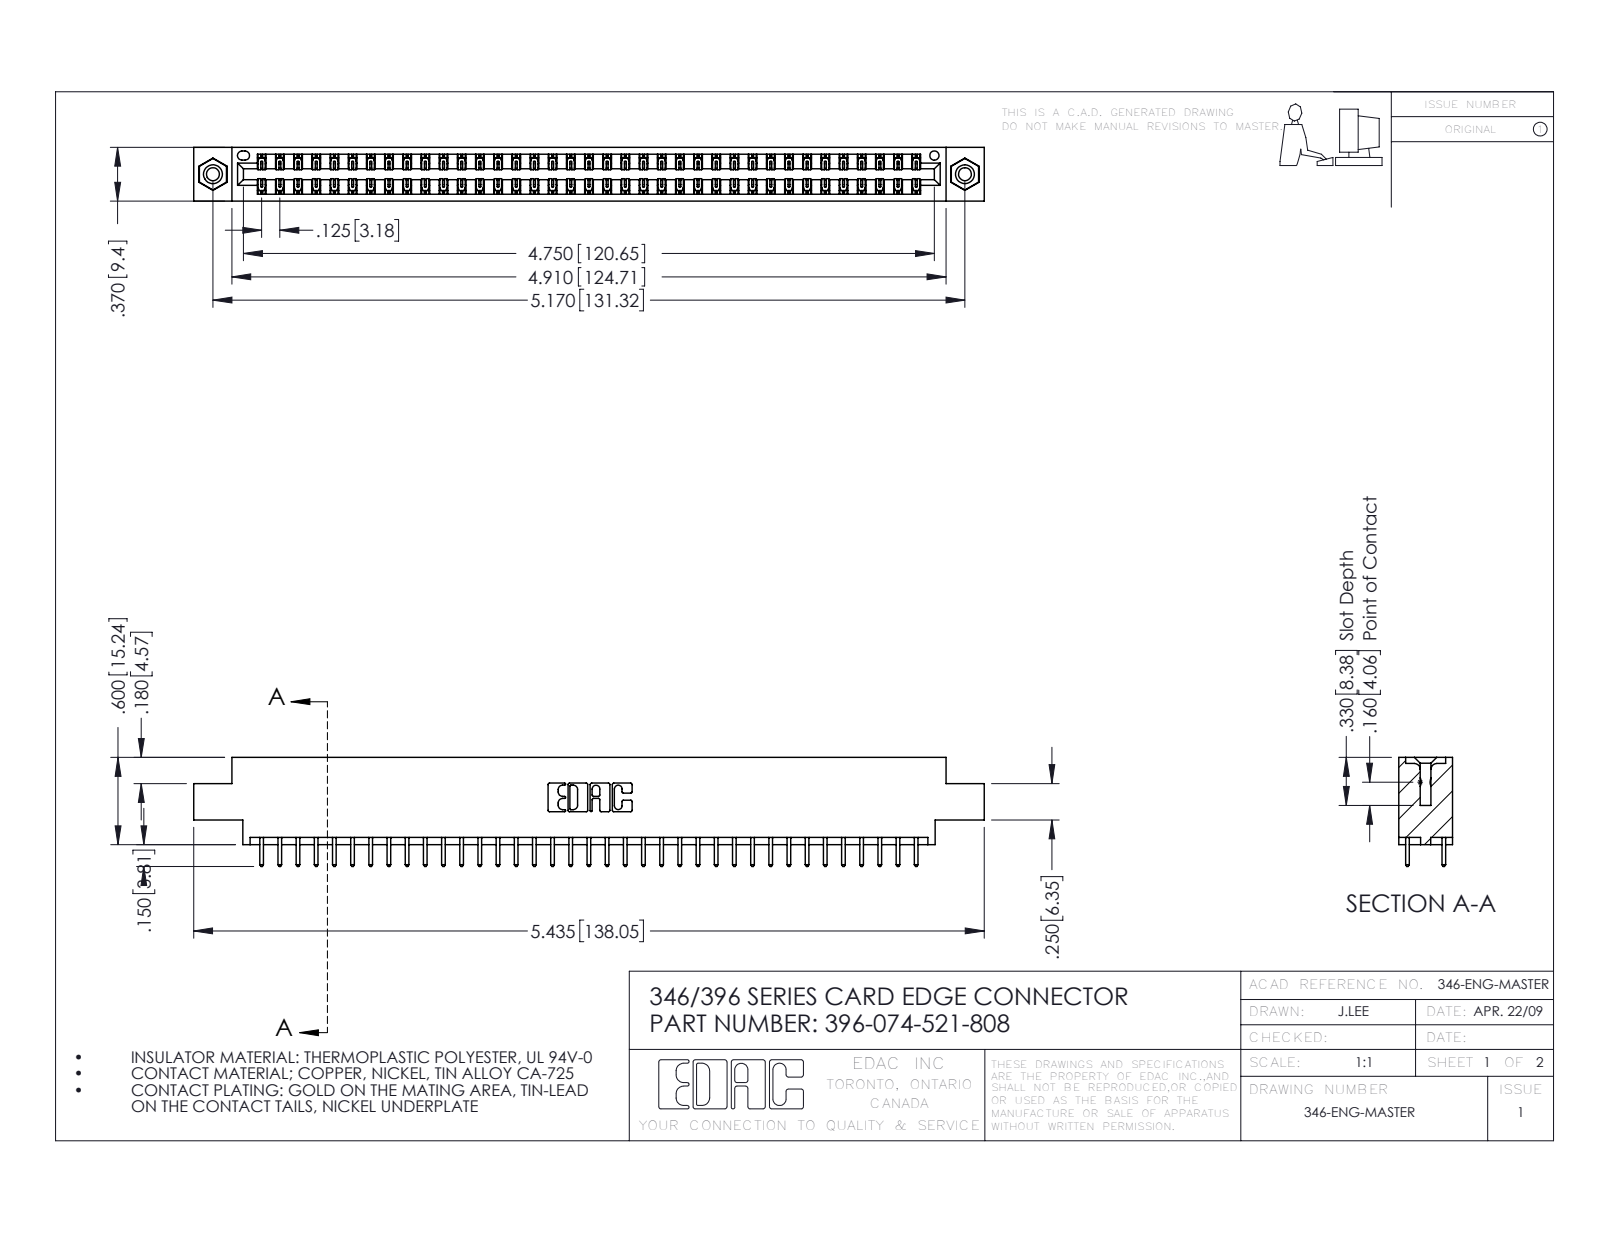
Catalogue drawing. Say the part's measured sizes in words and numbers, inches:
The part is named "396-074-521-808; 345-250-001_345-250-003-102; 346 Part_0.170 Offset - 0.156 Dia-TI; 345-292-001_345-293-121". Its 3-D file was written by "SolidWorks 2016 (CONFIG_CONTROL_DESIGN)". It is 77 solids with 4034 faces: 2702 planar, 1316 cylindrical and 16 other. Overall it measures 5.435 by 0.75 by 0.37 inches. Its volume is 0.807 cubic inches and its surface area 28.06 square inches. Round holes: 2 of diameter 0.089, 2 of diameter 0.125, 2 of diameter 0.156, 1 of diameter 0.064. Round bosses or shafts: 2 of diameter 0.155. Partial cylindrical surfaces (rounded edges, fillets, slot ends): 111 of radius 0.006, 74 of radius 0.01, 22 of radius 0.01, 6 of radius 0.007, 6 of radius 0.031, 3 of radius 0.026, 2 of radius 0.014, 2 of radius 0.022. The main face-to-face distances are 0.048, 0.322, 0.37, 0.25, 0.072, 0.298, 0.025, 0.275, 0.222, 0.148. The hole center spacings are 0.246, 4.961, 5.17.
